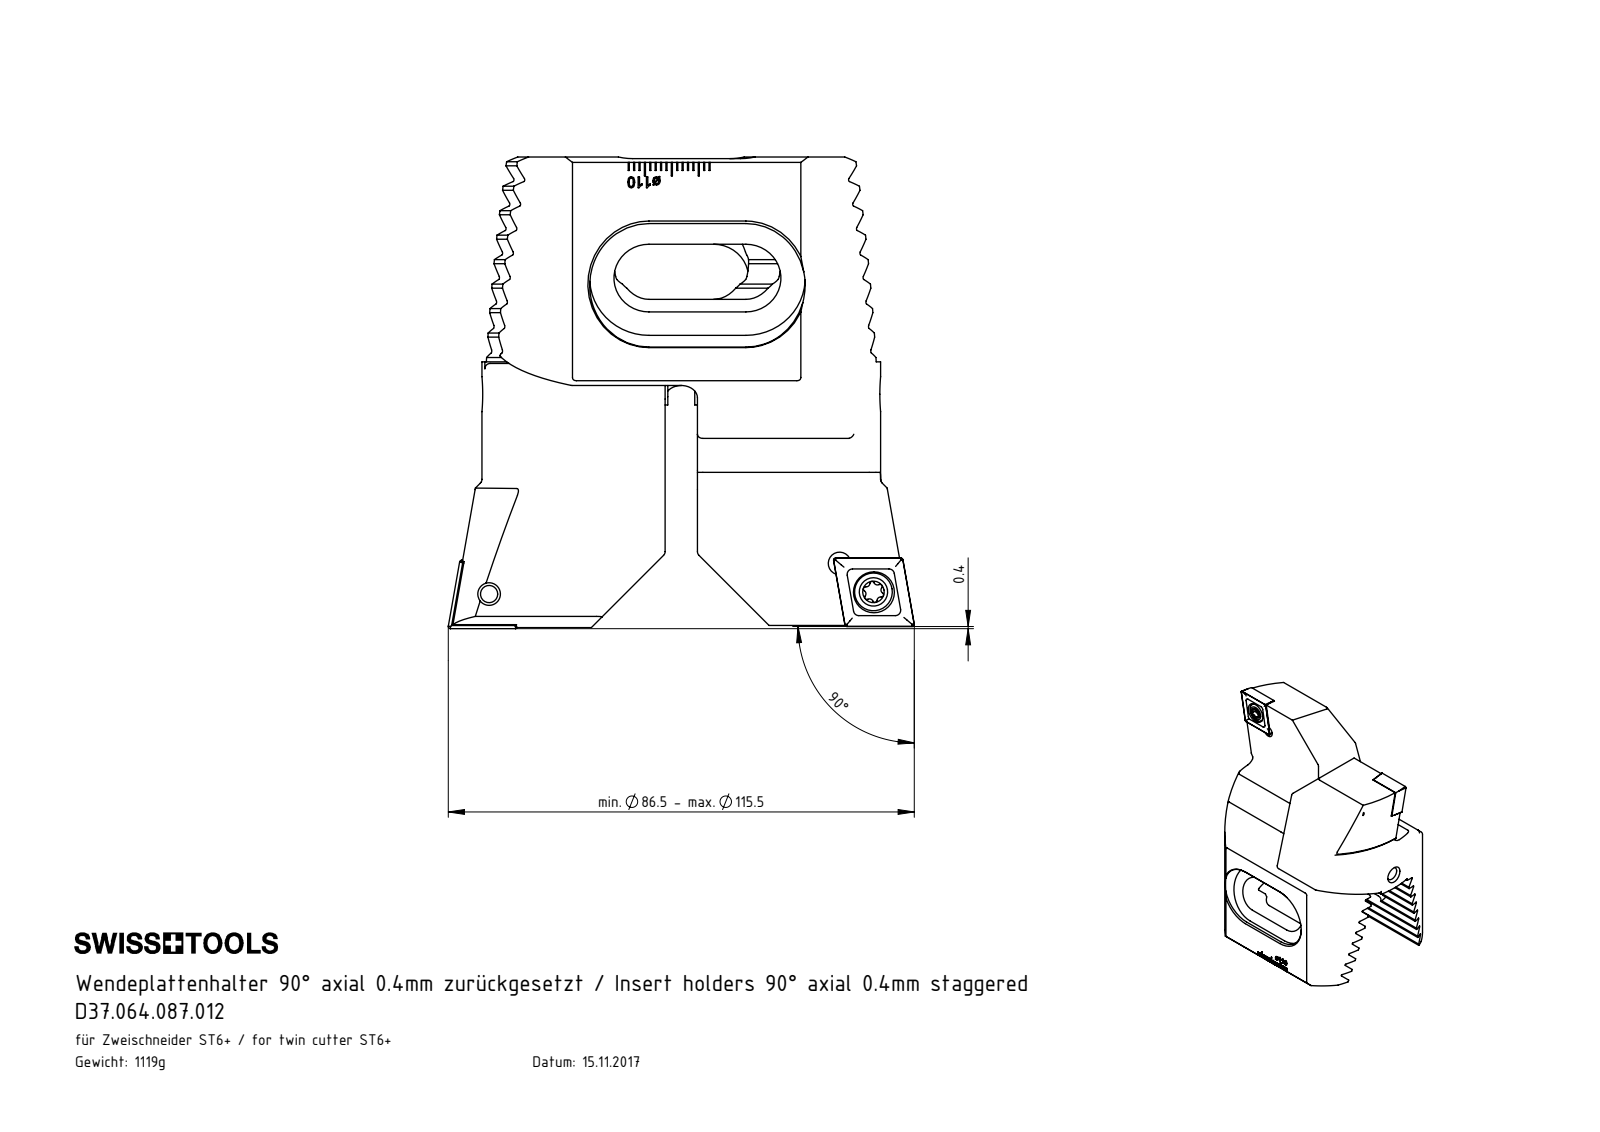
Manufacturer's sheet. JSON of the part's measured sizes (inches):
{"part_name": "ISO 4028 - M3 x 5_M3x8; CCMT120404; ZC7-xxx.001.050_A_versetzt Combi; WCC-ER2.001.010_A (+3 more)", "step_written_by": "SolidWorks 2017 (CONFIG_CONTROL_DESIGN)", "units": "inches", "bodies": {"solids": 8, "faces": 746, "planar": 411, "cylindrical": 143, "other": 192}, "overall_size": [3.445, 3.406, 2.291], "volume_in3": 8.682, "surface_area_in2": 57.7, "round_holes": [[0.165, 4], [0.197, 2], [0.217, 2], [0.299, 2], [0.079, 1], [0.098, 1], [0.315, 1]], "round_bosses_or_shafts": [[0.276, 2], [0.197, 2], [0.236, 1], [0.157, 1], [0.118, 1], [0.079, 1]], "partial_cylinders_radius": [[0.013, 16], [0.039, 16], [0.015, 12], [0.027, 6], [0.027, 6], [0.118, 4], [0.256, 4], [0.433, 4]], "face_to_face_distances": [0.16, 0.32, 0.802, 0.481, 1.134, 1.157, 2.291, 0.641, 0.801, 0.962], "hole_center_spacings": [0.323, 0.328, 2.812, 0.787, 2.313, 2.568, 2.571, 2.572]}
